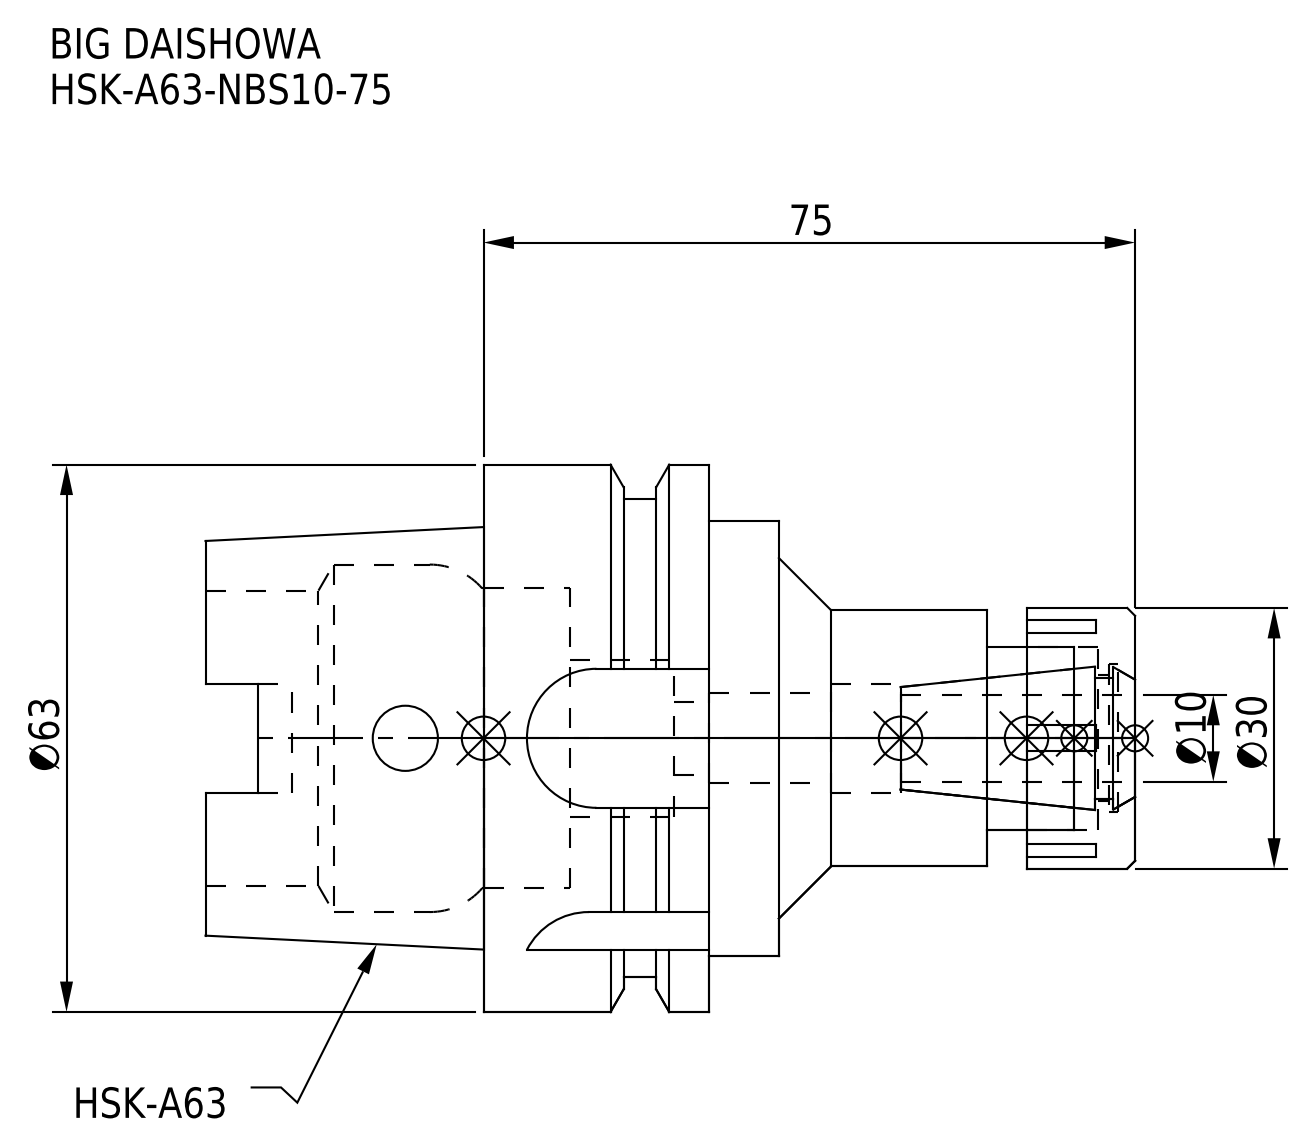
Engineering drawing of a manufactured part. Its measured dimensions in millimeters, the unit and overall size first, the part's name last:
Units: millimetres
Overall size (bounding box): 107 × 63 × 63
Round holes (diameter × count): ⌀7.5 ×1, ⌀8.4 ×1, ⌀10.4 ×1, ⌀12.5 ×1, ⌀14.5 ×1, ⌀17 ×1, ⌀18 ×1, ⌀21 ×1, ⌀34 ×1, ⌀34.5 ×1, ⌀40 ×1
Round bosses / shafts (diameter × count): ⌀63 ×1, ⌀55 ×1, ⌀50 ×1, ⌀30 ×1, ⌀29.5 ×1
Partial cylindrical surfaces — rounded edges, fillets, slot ends (radius × count): R2.88 ×4, R8 ×4
Main face-to-face distances: 26, 32, 58, 34, 16.05, 9.95, 8, 24.05, 41, 49
Volume: 118 802 mm³ · Surface area: 31 039 mm²
Bodies: 2 solids, 141 faces (70 planar, 49 cylindrical, 22 other)
Part name (STEP PRODUCT): NBN10_1.stp; HSK-A63-NBS10-75_1.stp; HSK-A63-NBS10-75-FreeParts; DXF_TEMP_ASSY_ASM_4_ASM.stp (+3 more)
STEP written by: SolidWorks 2019 (CONFIG_CONTROL_DESIGN)
